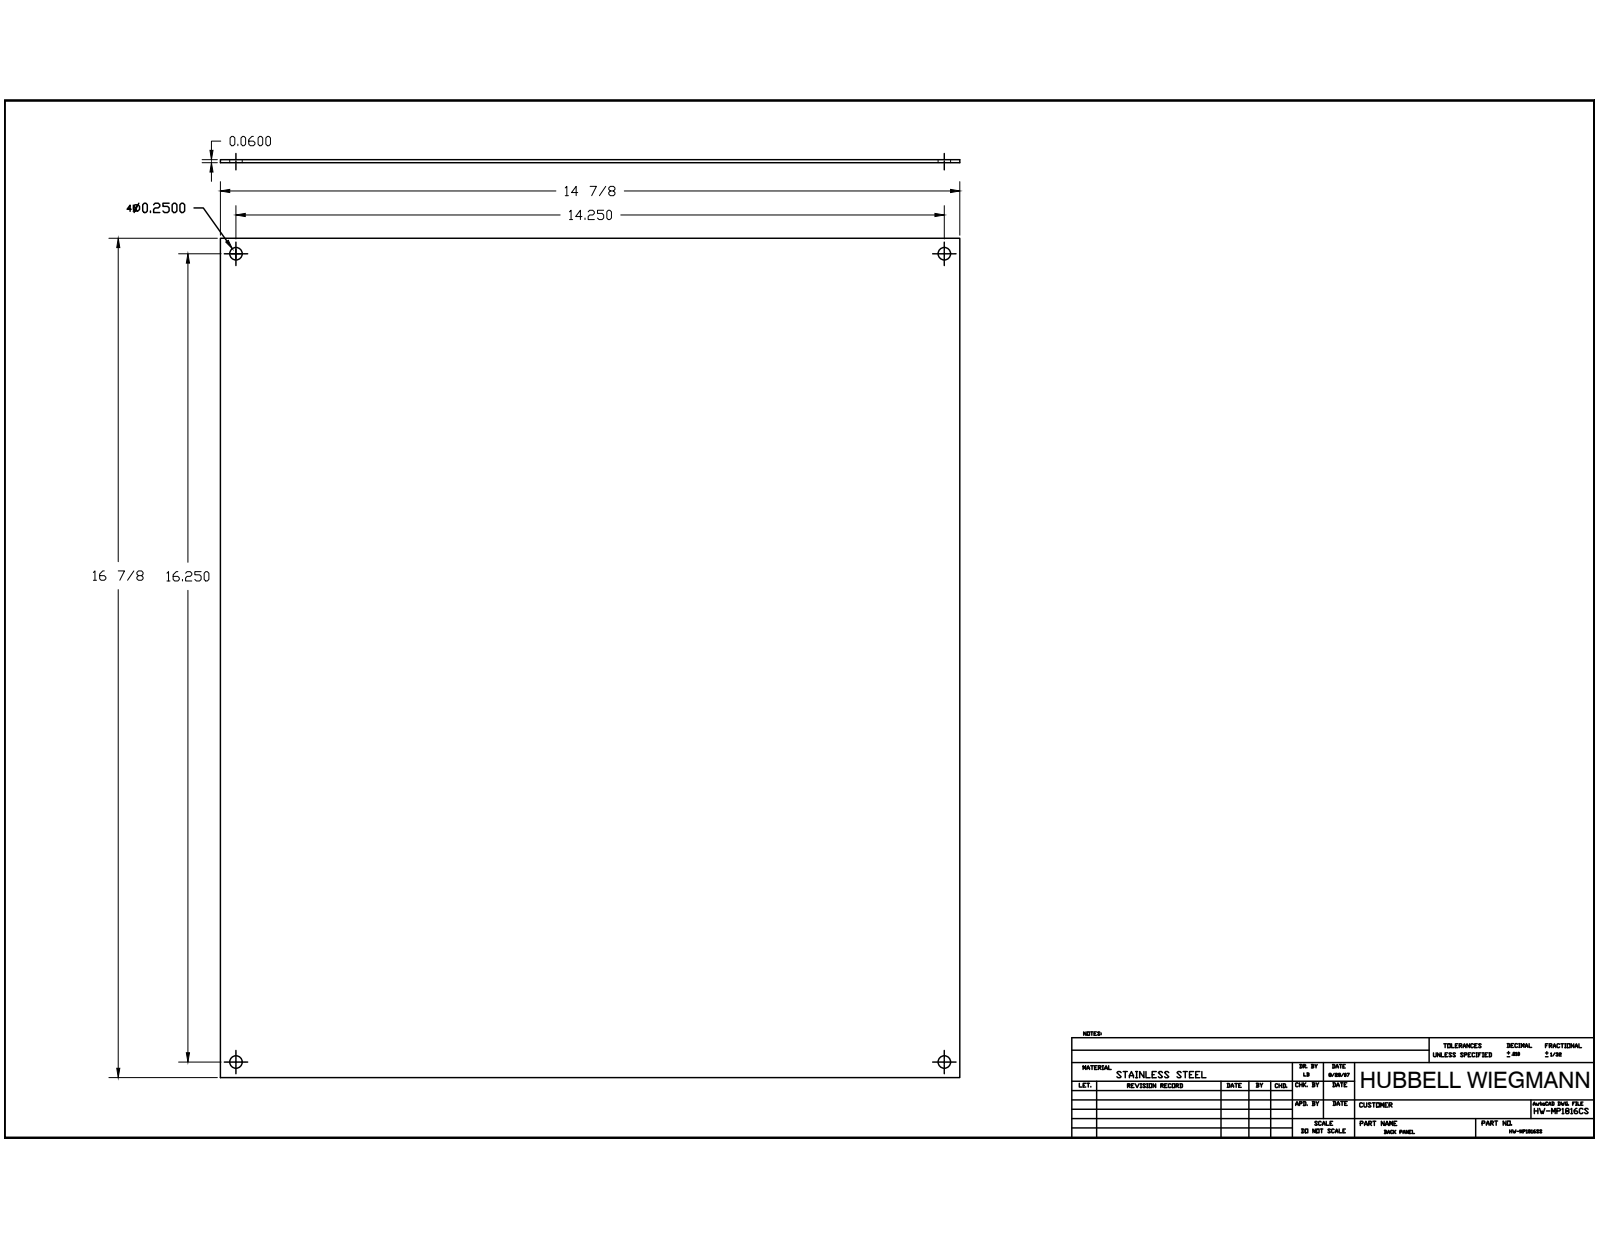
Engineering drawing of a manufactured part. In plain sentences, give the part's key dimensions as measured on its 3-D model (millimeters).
The part is named "BP1816SS_STP". Its 3-D file was written by "Autodesk Inventor 2014 (AUTOMOTIVE_DESIGN)". It is 1 solid with 10 faces: 6 planar, 4 cylindrical and 0 other. Overall it measures 428.62 by 377.82 by 1.52 millimeters. Its volume is 246 611 cubic millimeters and its surface area 326 217 square millimeters. Round holes: 4 of diameter 6.35. The main face-to-face distances are 1.52, 377.82, 428.62. The hole center spacings are 361.94, 412.76, 548.97.
